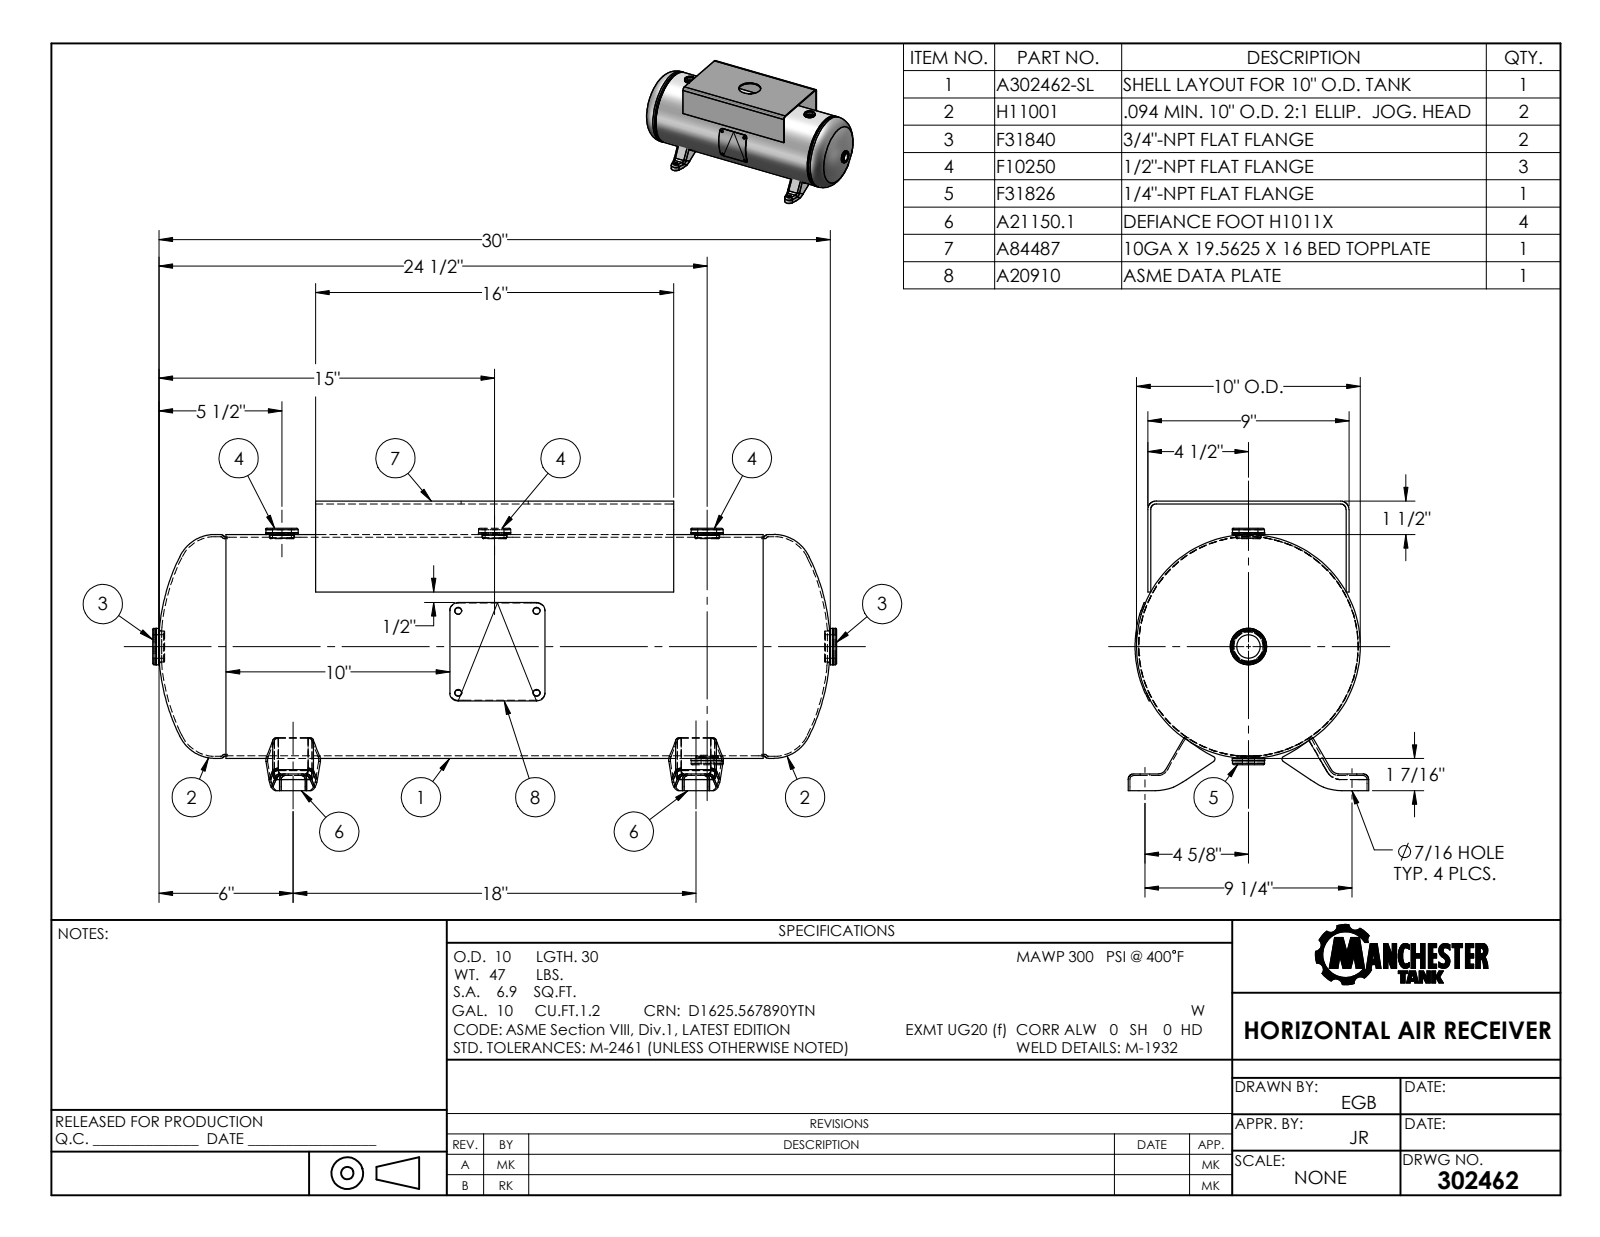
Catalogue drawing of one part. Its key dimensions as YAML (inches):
part_name: "302462"
step_written_by: "SolidWorks 2011 (CONFIG_CONTROL_DESIGN)"
units: inches
bodies: {solids: 0, faces: 359, planar: 97, cylindrical: 108, other: 154}
overall_size: [31.188, 12.96, 10.75]
round_holes:
  - {diameter: 0.437, count: 4}
  - {diameter: 0.84, count: 3}
  - {diameter: 0.54, count: 1}
  - {diameter: 1, count: 1}
  - {diameter: 1.05, count: 1}
  - {diameter: 3, count: 1}
round_bosses_or_shafts:
  - {diameter: 1.813, count: 2}
  - {diameter: 10, count: 1}
  - {diameter: 9.79, count: 1}
  - {diameter: 2.062, count: 1}
  - {diameter: 1.5, count: 1}
  - {diameter: 1.438, count: 1}
partial_cylinders:
  - {radius: 0.25, count: 12}
  - {radius: 0.16, count: 8}
  - {radius: 0.41, count: 4}
  - {radius: 0.5, count: 4}
  - {radius: 0.125, count: 2}
  - {radius: 0.34, count: 2}
  - {radius: 0.384, count: 2}
  - {radius: 1.209, count: 2}
face_to_face_distances: [0.135, 8.865, 9, 8.731, 0.09, 4, 20, 3.928, 4.063, 17.406]
hole_center_spacings: [4.652, 10.119, 19.069, 9.25, 9.5, 18, 20.238, 19]
